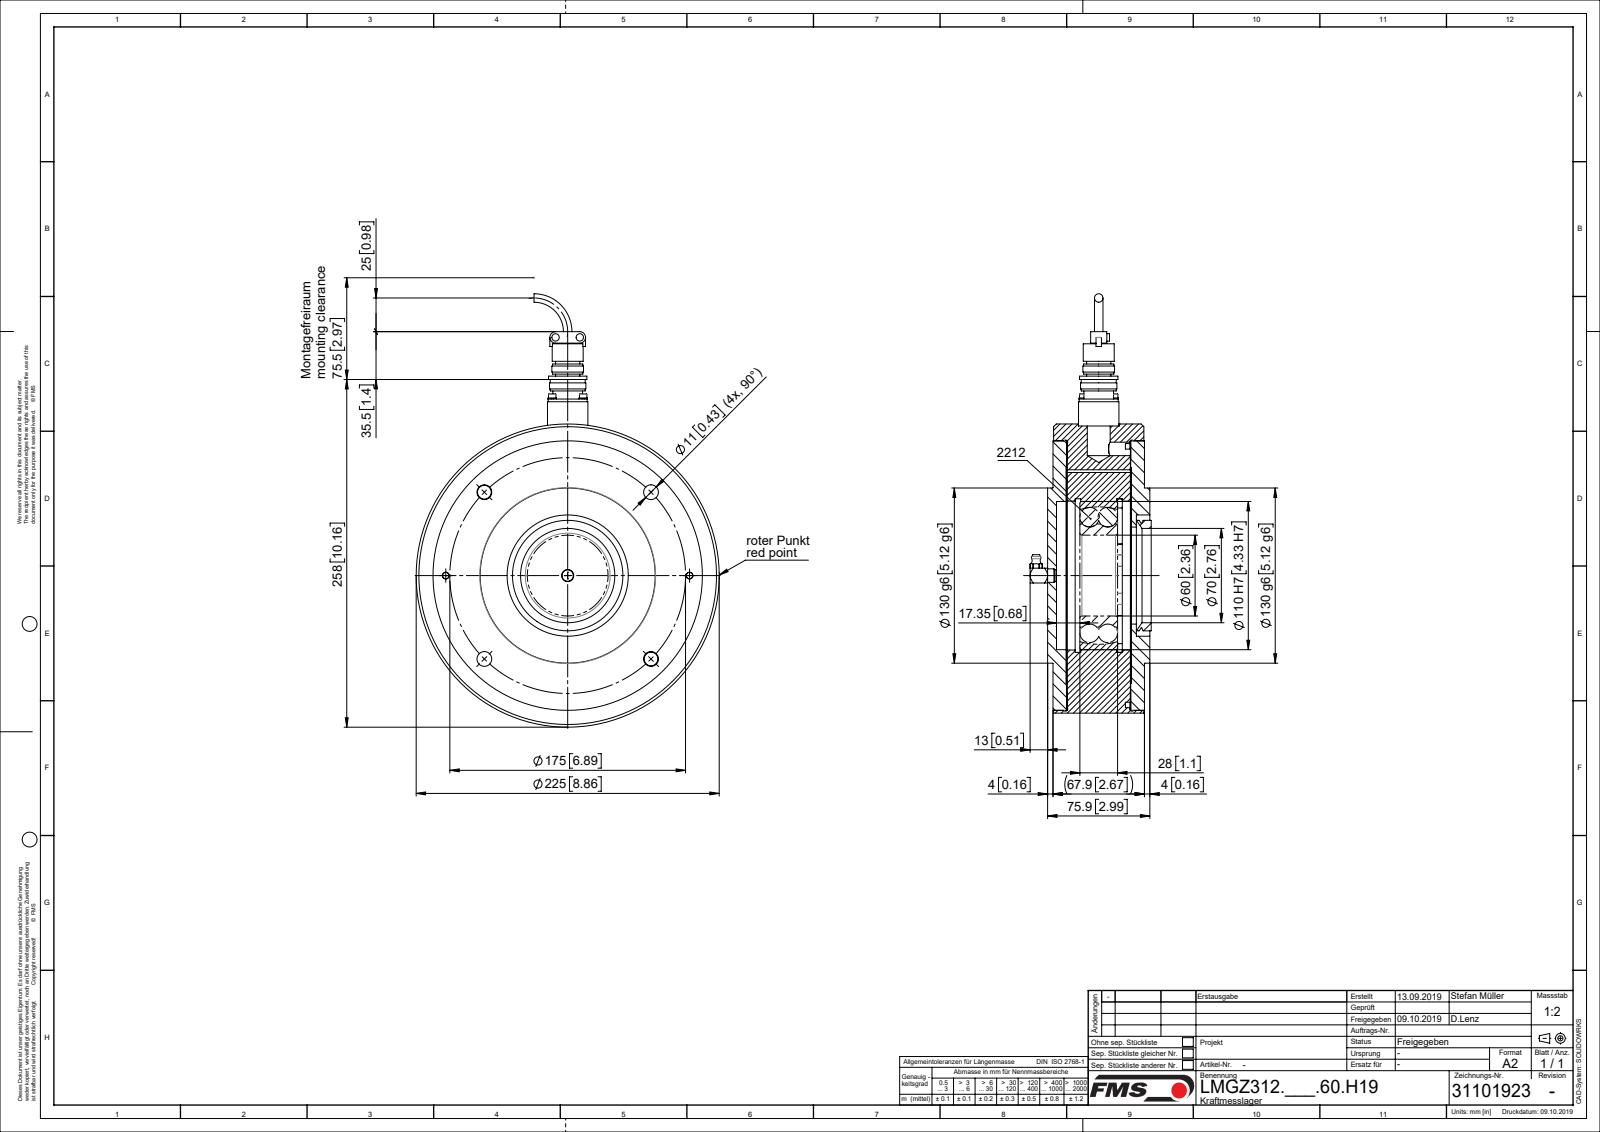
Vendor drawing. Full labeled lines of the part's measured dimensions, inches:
Part name (STEP PRODUCT): ZEICHNUNG8; L50036; L4765504; TEIL1 (+8 more)
STEP written by: Mechanical Desktop 2009 (CONFIG_CONTROL_DESIGN)
Units: inches
Bodies: 21 solids, 428 faces (122 planar, 238 cylindrical, 68 other)
Overall size (bounding box): 12.663 × 8.858 × 3.559
Volume: 145.2 in³ · Surface area: 609.1 in²
Round holes (diameter × count): ⌀0.433 ×6, ⌀0.354 ×5, ⌀0.102 ×4, ⌀0.126 ×4, ⌀0.134 ×4, ⌀0.197 ×2, ⌀0.26 ×2, ⌀0.402 ×2, ⌀0.906 ×1, ⌀2.362 ×1, ⌀2.756 ×1, ⌀2.835 ×1
Round bosses / shafts (diameter × count): ⌀0.217 ×6, ⌀0.244 ×4, ⌀0.118 ×4, ⌀0.098 ×4, ⌀0.394 ×3, ⌀0.236 ×2, ⌀8.858 ×1, ⌀7.835 ×1
Partial cylindrical surfaces — rounded edges, fillets, slot ends (radius × count): R0.167 ×2, R3.189 ×1, R3.386 ×1
Main face-to-face distances: 1.86, 0.411, 0.402, 2.262, 2.272, 1.87, 0.384, 0.02, 1.89, 0.382
Hole centre spacings: 0.64, 0.906, 2.684, 3.445, 4.872, 6.474, 1.281, 3.563
